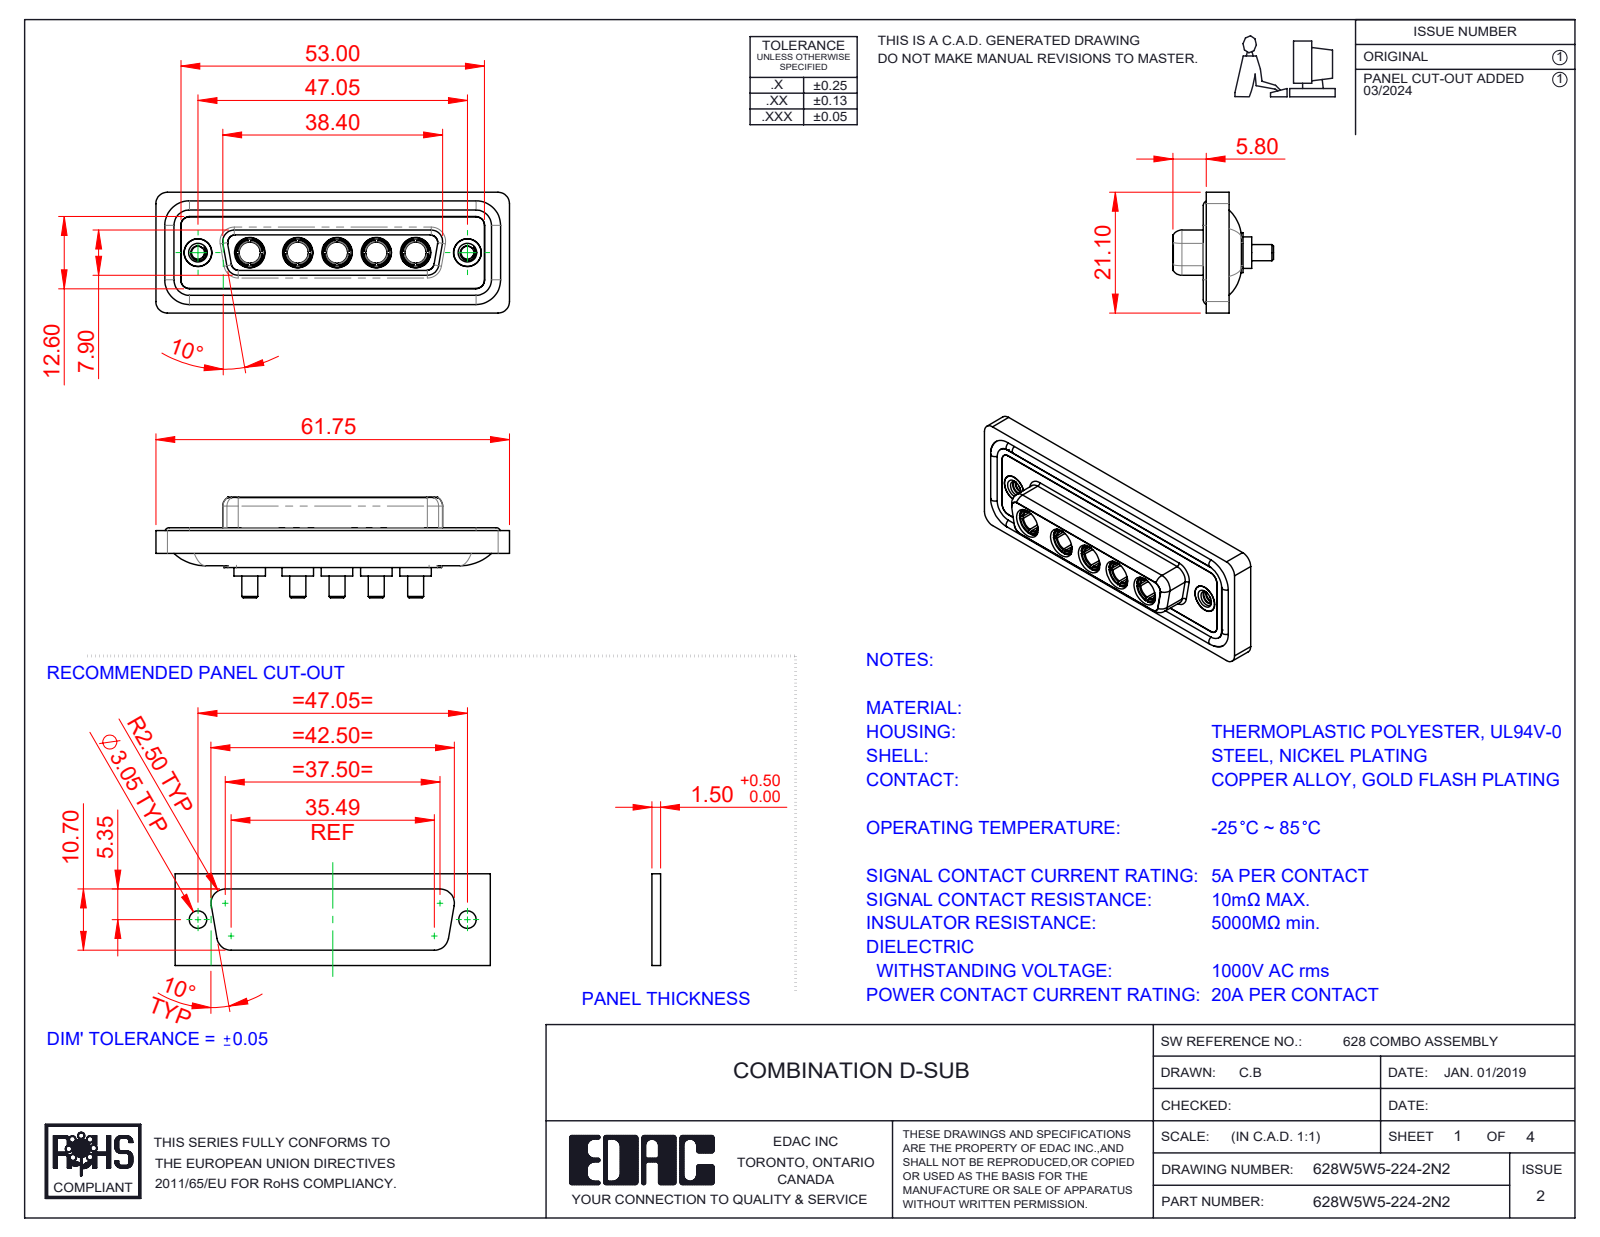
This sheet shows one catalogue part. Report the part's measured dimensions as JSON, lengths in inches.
{"part_name": "628Combo Shell Rear_25 Contacts; 628Combo Housing_5W5; 628Combo Threaded Rivet_2; 628Combo Shell Front_25 Contacts (+3 more)", "step_written_by": "SolidWorks 2023 (CONFIG_CONTROL_DESIGN)", "units": "inches", "bodies": {"solids": 17, "faces": 756, "planar": 250, "cylindrical": 303, "other": 203}, "overall_size": [2.431, 0.831, 0.691], "volume_in3": 0.499, "surface_area_in2": 20.79, "round_holes": [[0.191, 7], [0.146, 5], [0.209, 5], [0.089, 2], [0.157, 2], [0.159, 2], [0.197, 2]], "round_bosses_or_shafts": [[0.217, 5], [0.205, 5], [0.195, 5], [0.187, 5], [0.148, 5], [0.11, 5], [0.063, 4], [0.195, 2]], "partial_cylinders_radius": [[0.059, 22], [0.079, 18], [0.053, 8], [0.063, 8], [0.083, 5], [0.01, 4], [0.02, 4], [0.024, 4]], "face_to_face_distances": [0.016, 0.071, 0.293, 0.222, 0.02, 0.278, 0.26, 0.063, 0.043, 0.114], "hole_center_spacings": [0.27, 0.356, 0.54, 1.496, 0.33, 0.6, 0.626, 0.686]}
